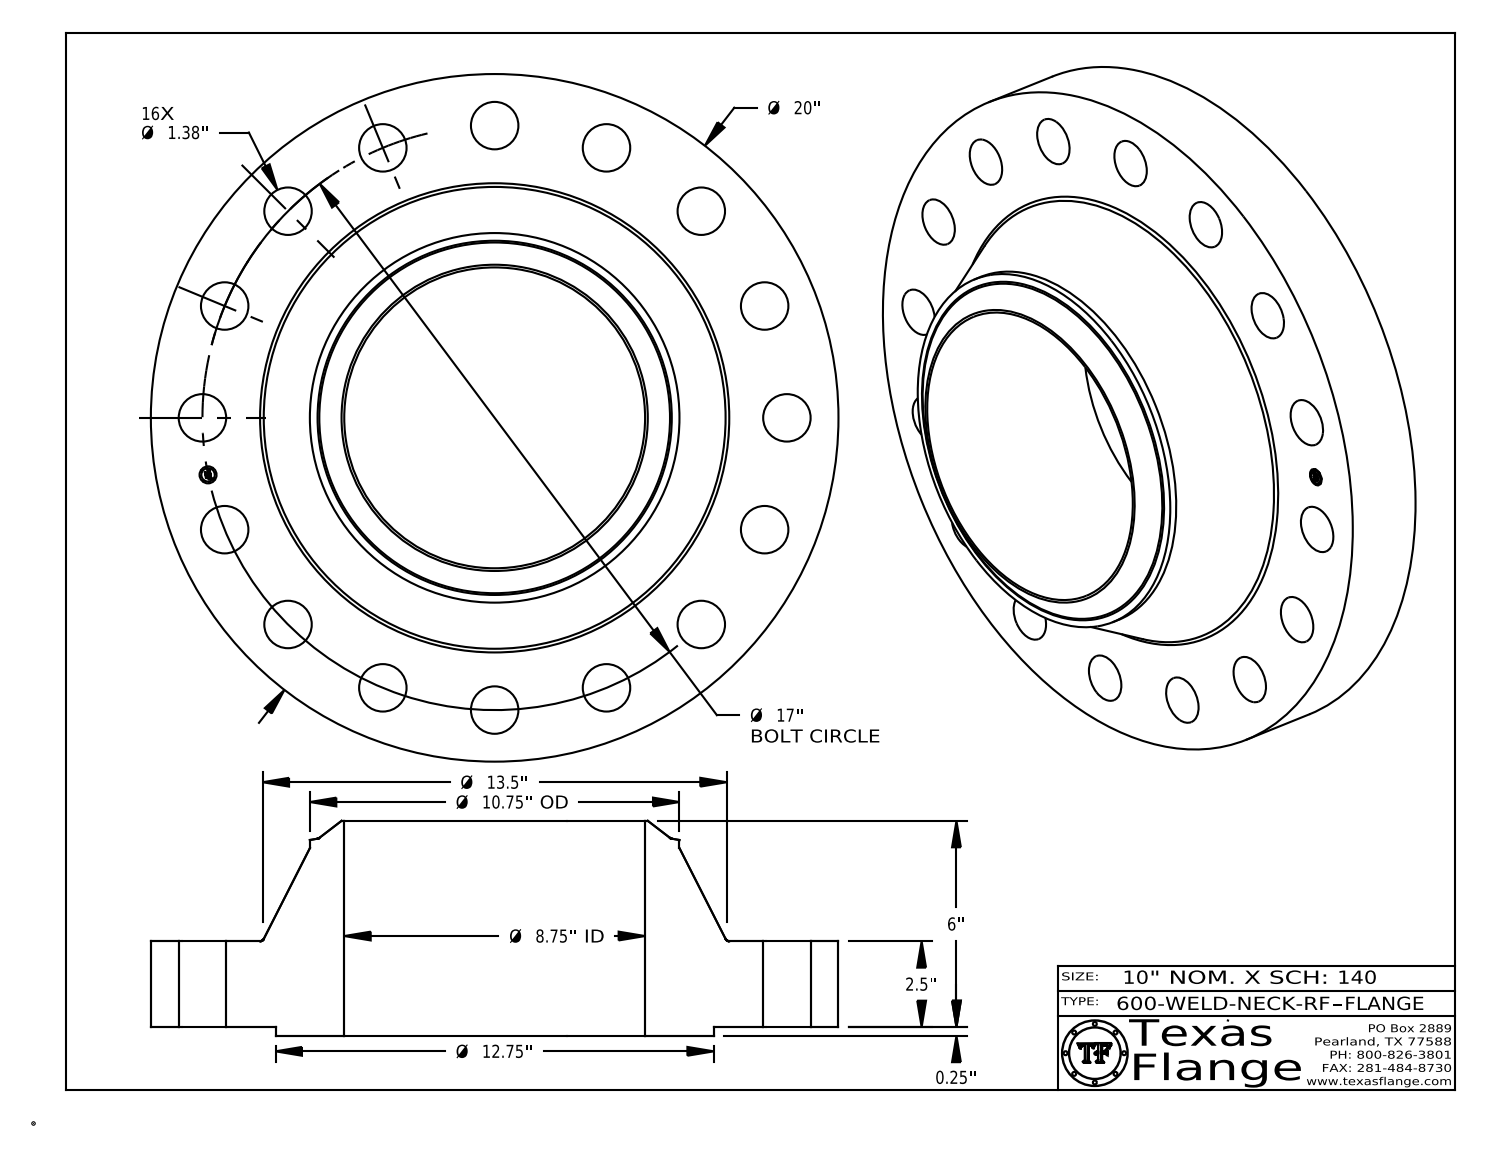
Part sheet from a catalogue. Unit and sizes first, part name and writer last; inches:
Units: inches
Overall size (bounding box): 20 × 20 × 6.25
Round holes (diameter × count): ⌀1.38 ×16, ⌀0.495 ×1, ⌀8.75 ×1
Round bosses / shafts (diameter × count): ⌀0.03 ×8, ⌀20 ×1, ⌀12.75 ×1, ⌀10.75 ×1, ⌀0.39 ×1
Main face-to-face distances: 2.5, 0.25, 2.75, 6.25, 6, 3.5, 2.735, 2.485, 0.015, 3.515
Hole centre spacings: 3.317, 14.135, 8.5, 6.506, 12.021, 9.444, 9.445, 15.706
Volume: 757.8 in³ · Surface area: 1 049 in²
Bodies: 1 solid, 439 faces (369 planar, 60 cylindrical, 10 other)
Part name (STEP PRODUCT): 600-WELD-NECK-RF
STEP written by: CATIA V5 STEP AP214 (AUTOMOTIVE_DESIGN)
